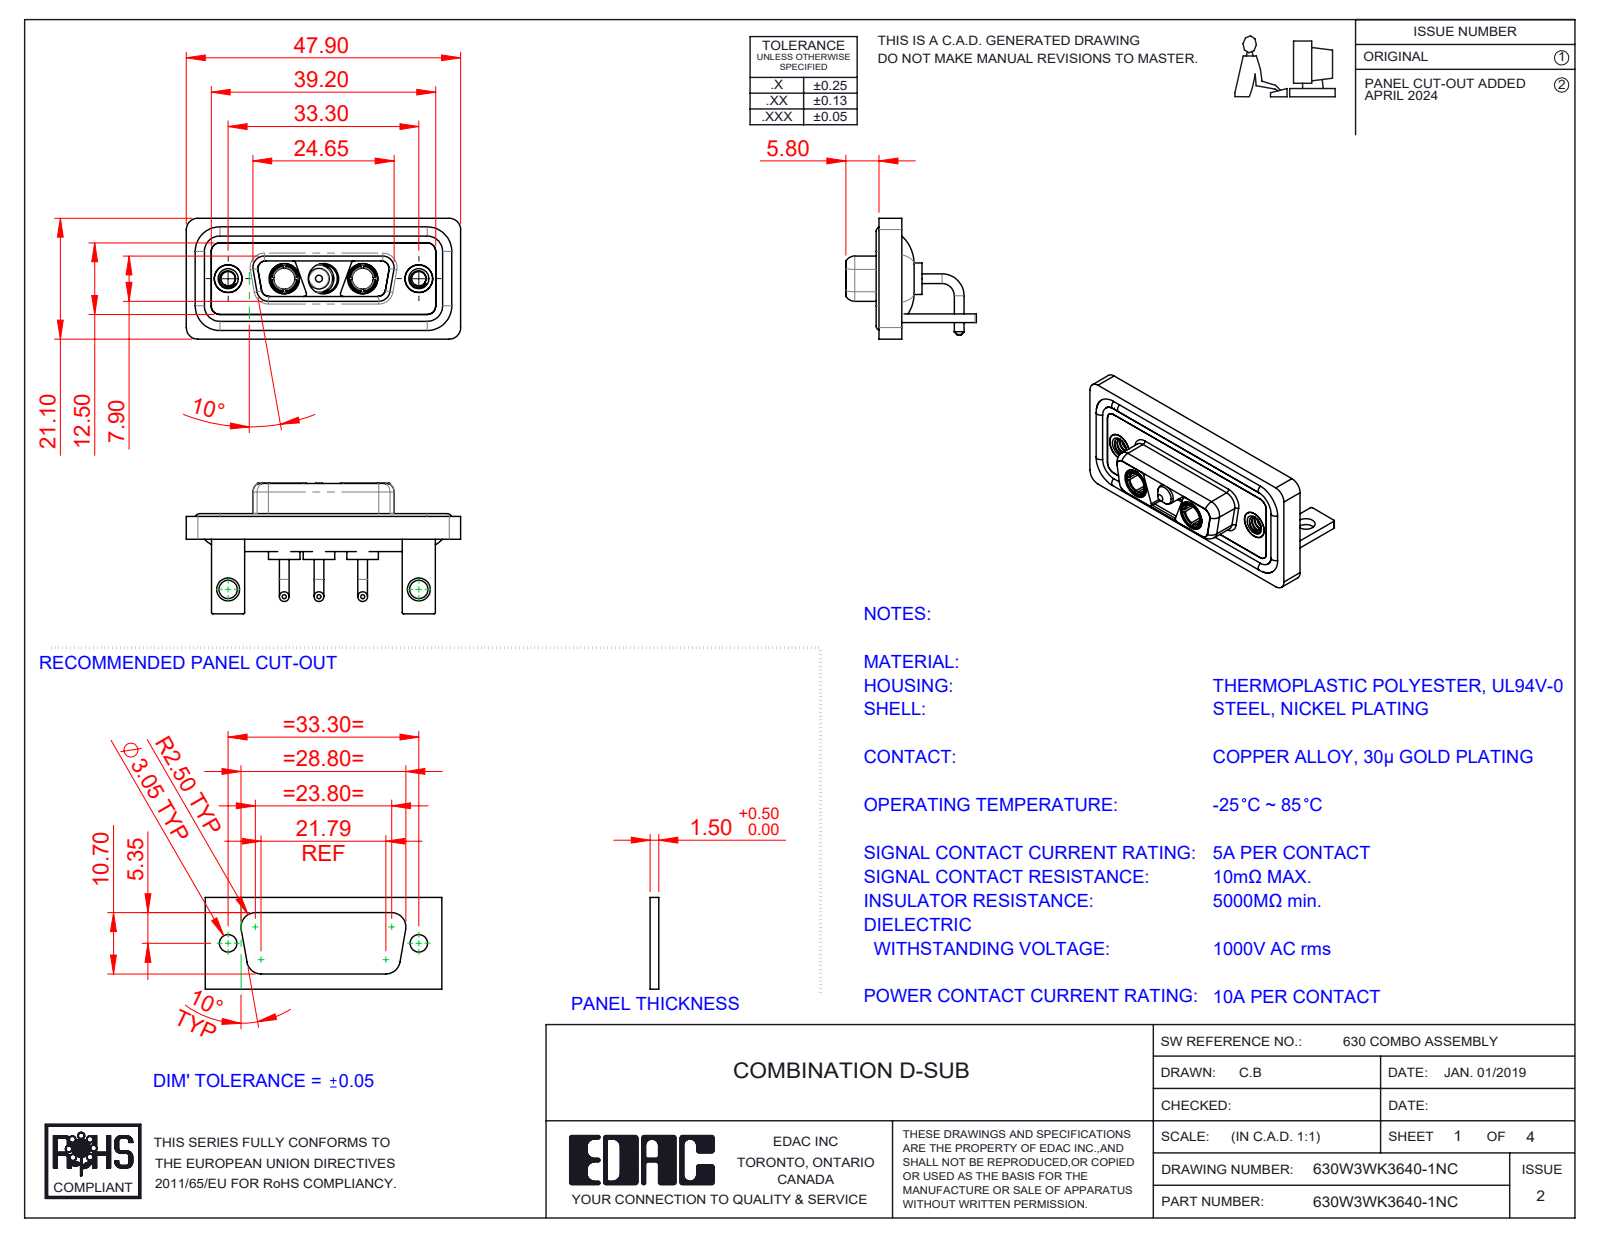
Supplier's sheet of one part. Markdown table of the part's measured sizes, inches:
| quantity | value |
| --- | --- |
| part name | 630Combo Shell Front_15 Contacts; 630Combo Stabilizer Bracket_50 Contacts; Power Pin_10A RA; Power Socket_10A RA (+5 more) |
| STEP written by | SolidWorks 2023 (CONFIG_CONTROL_DESIGN) |
| units | inches |
| bodies | 15 solids, 637 faces (198 planar, 286 cylindrical, 153 other) |
| overall size | 1.886 × 0.898 × 0.831 |
| volume | 0.379 in³ |
| surface area | 16 in² |
| round holes (diameter × count) | 0.191 × 5, 0.209 × 3, 0.098 × 2, 0.126 × 2, 0.146 × 2, 0.157 × 2, 0.159 × 2, 0.197 × 2 |
| round bosses / shafts (diameter × count) | 0.067 × 6, 0.063 × 4, 0.217 × 3, 0.205 × 3, 0.187 × 3, 0.148 × 3, 0.195 × 2, 0.195 × 2 |
| partial cylindrical surfaces (radius × count) | 0.079 × 21, 0.059 × 18, 0.01 × 16, 0.053 × 12, 0.02 × 9, 0.063 × 8, 0.024 × 4, 0.026 × 4 |
| main face-to-face distances | 0.016, 0.114, 0.059, 0.146, 0.071, 0.043, 0.161, 0.063, 0.098, 0.055 |
| hole center spacings | 0.27, 0.386, 0.656, 0.925, 1.311, 0.539 |
